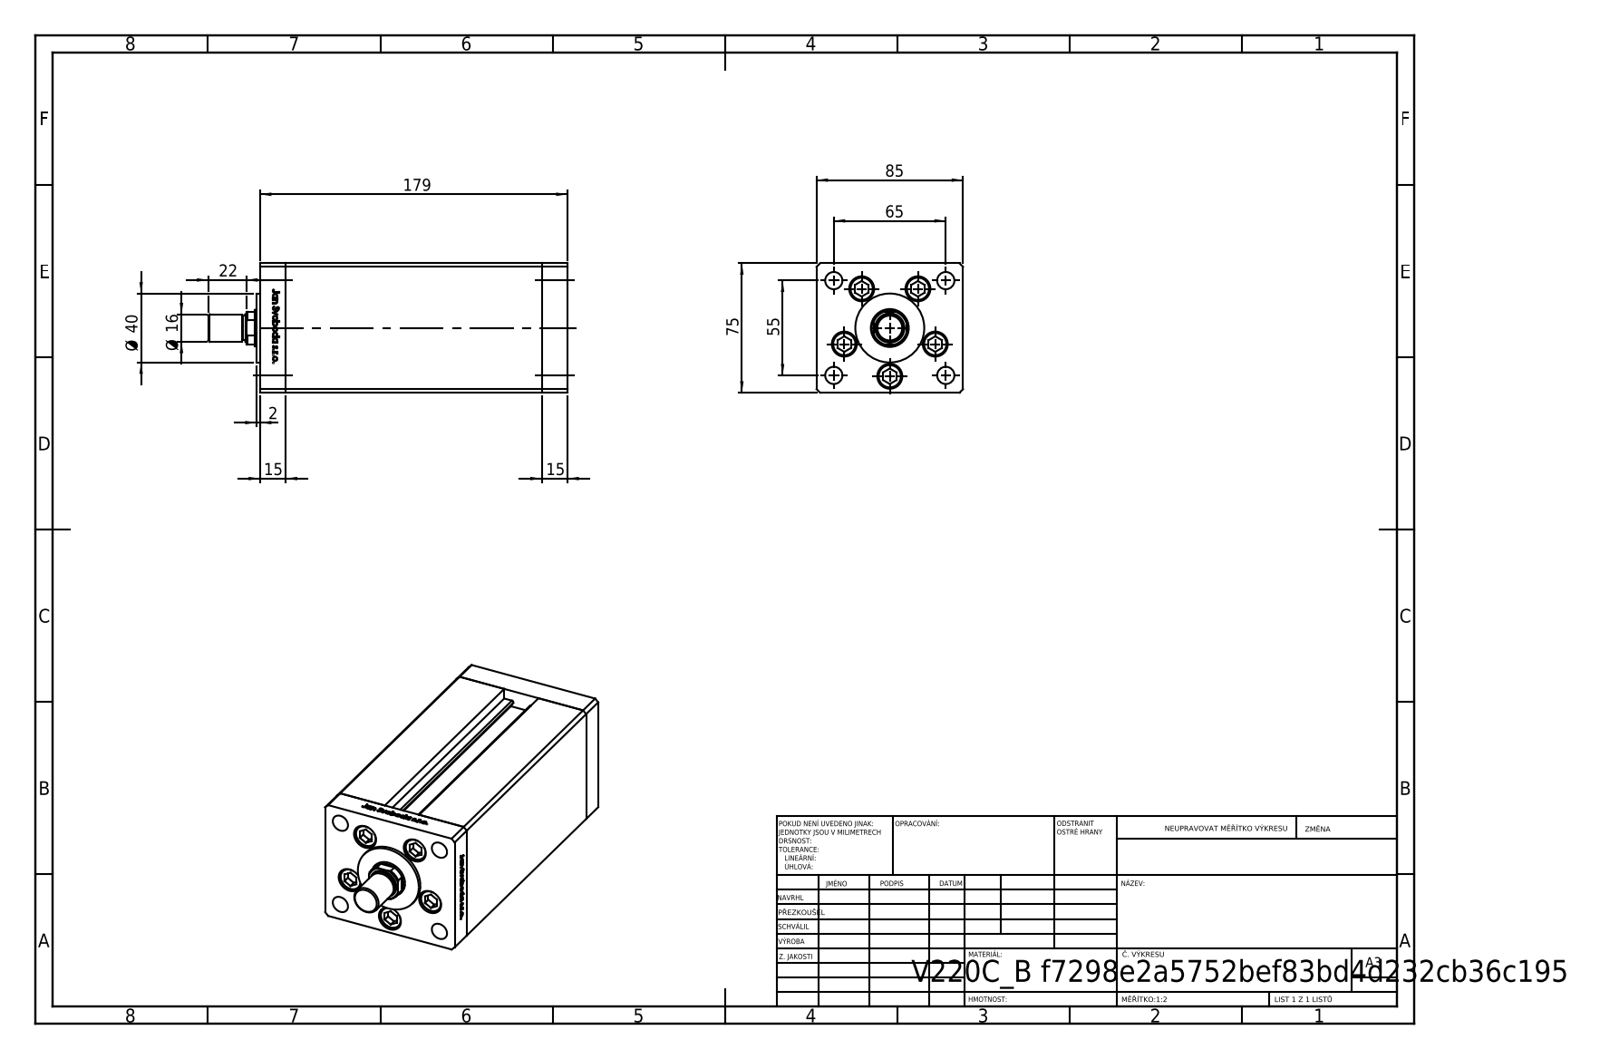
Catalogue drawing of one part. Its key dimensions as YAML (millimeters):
part_name: "V220CC_MALE_METRIC; V220C_FRONT_B; V220C_B_VC; ALLEN BOLT (+2 more)"
step_written_by: "SolidWorks 2019 (CONFIG_CONTROL_DESIGN)"
units: millimeters
bodies: {solids: 15, faces: 1191, planar: 466, cylindrical: 147, other: 578}
overall_size: [208.5, 85, 75]
volume: 1014000
surface_area: 159786
round_holes:
  - {diameter: 11, count: 5}
  - {diameter: 14.5, count: 5}
  - {diameter: 10, count: 4}
  - {diameter: 2, count: 2}
  - {diameter: 13.16, count: 2}
  - {diameter: 15, count: 1}
  - {diameter: 22, count: 1}
round_bosses_or_shafts:
  - {diameter: 8, count: 5}
  - {diameter: 40, count: 1}
  - {diameter: 16, count: 1}
  - {diameter: 14, count: 1}
partial_cylinders:
  - {radius: 0.93, count: 2}
  - {radius: 10.5, count: 1}
face_to_face_distances: [85, 75, 148.5, 15, 163.5, 178.5, 68.5, 9, 64.5, 10.5]
hole_center_spacings: [28, 42.57, 16.86, 19.17, 32.33, 32.5, 33.63, 37.33]
